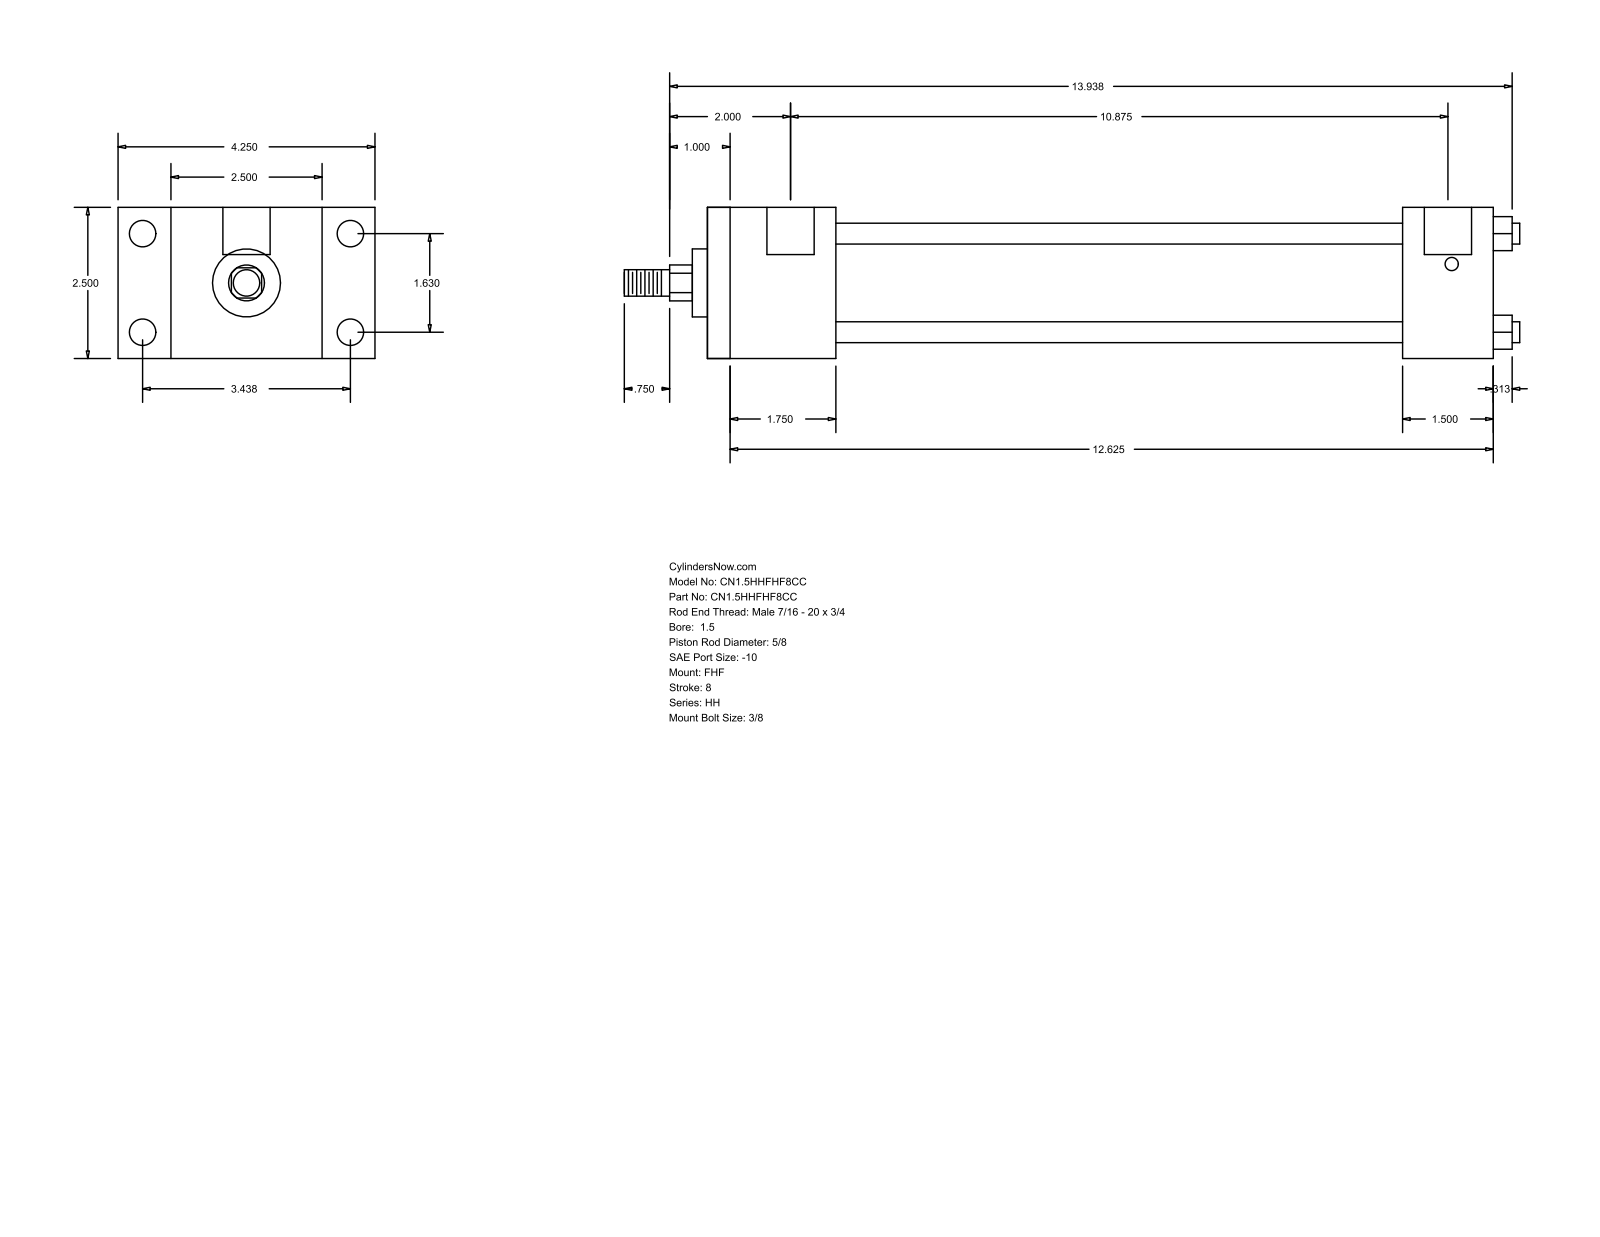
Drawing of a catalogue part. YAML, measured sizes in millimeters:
part_name: "HH_FHF__0150_0.625"
step_written_by: "GSSL Pune (CONFIG_CONTROL_DESIGN)"
units: millimeters
bodies: {solids: 0, faces: 88, planar: 60, cylindrical: 28, other: 0}
overall_size: [376.24, 107.95, 63.5]
round_holes:
  - {diameter: 5.56, count: 4}
  - {diameter: 11.13, count: 4}
  - {diameter: 19.84, count: 2}
round_bosses_or_shafts:
  - {diameter: 8.76, count: 4}
  - {diameter: 44.45, count: 1}
  - {diameter: 28.57, count: 1}
  - {diameter: 15.88, count: 1}
  - {diameter: 11.11, count: 1}
partial_cylinders:
  - {radius: 7.54, count: 1}
face_to_face_distances: [63.5, 22.23, 85.73, 53.97, 107.96, 330.19, 276.22, 292.1, 238.13, 38.09]
hole_center_spacings: [1.59, 41.4, 87.32, 96.64, 277.81, 279.4, 276.22]
